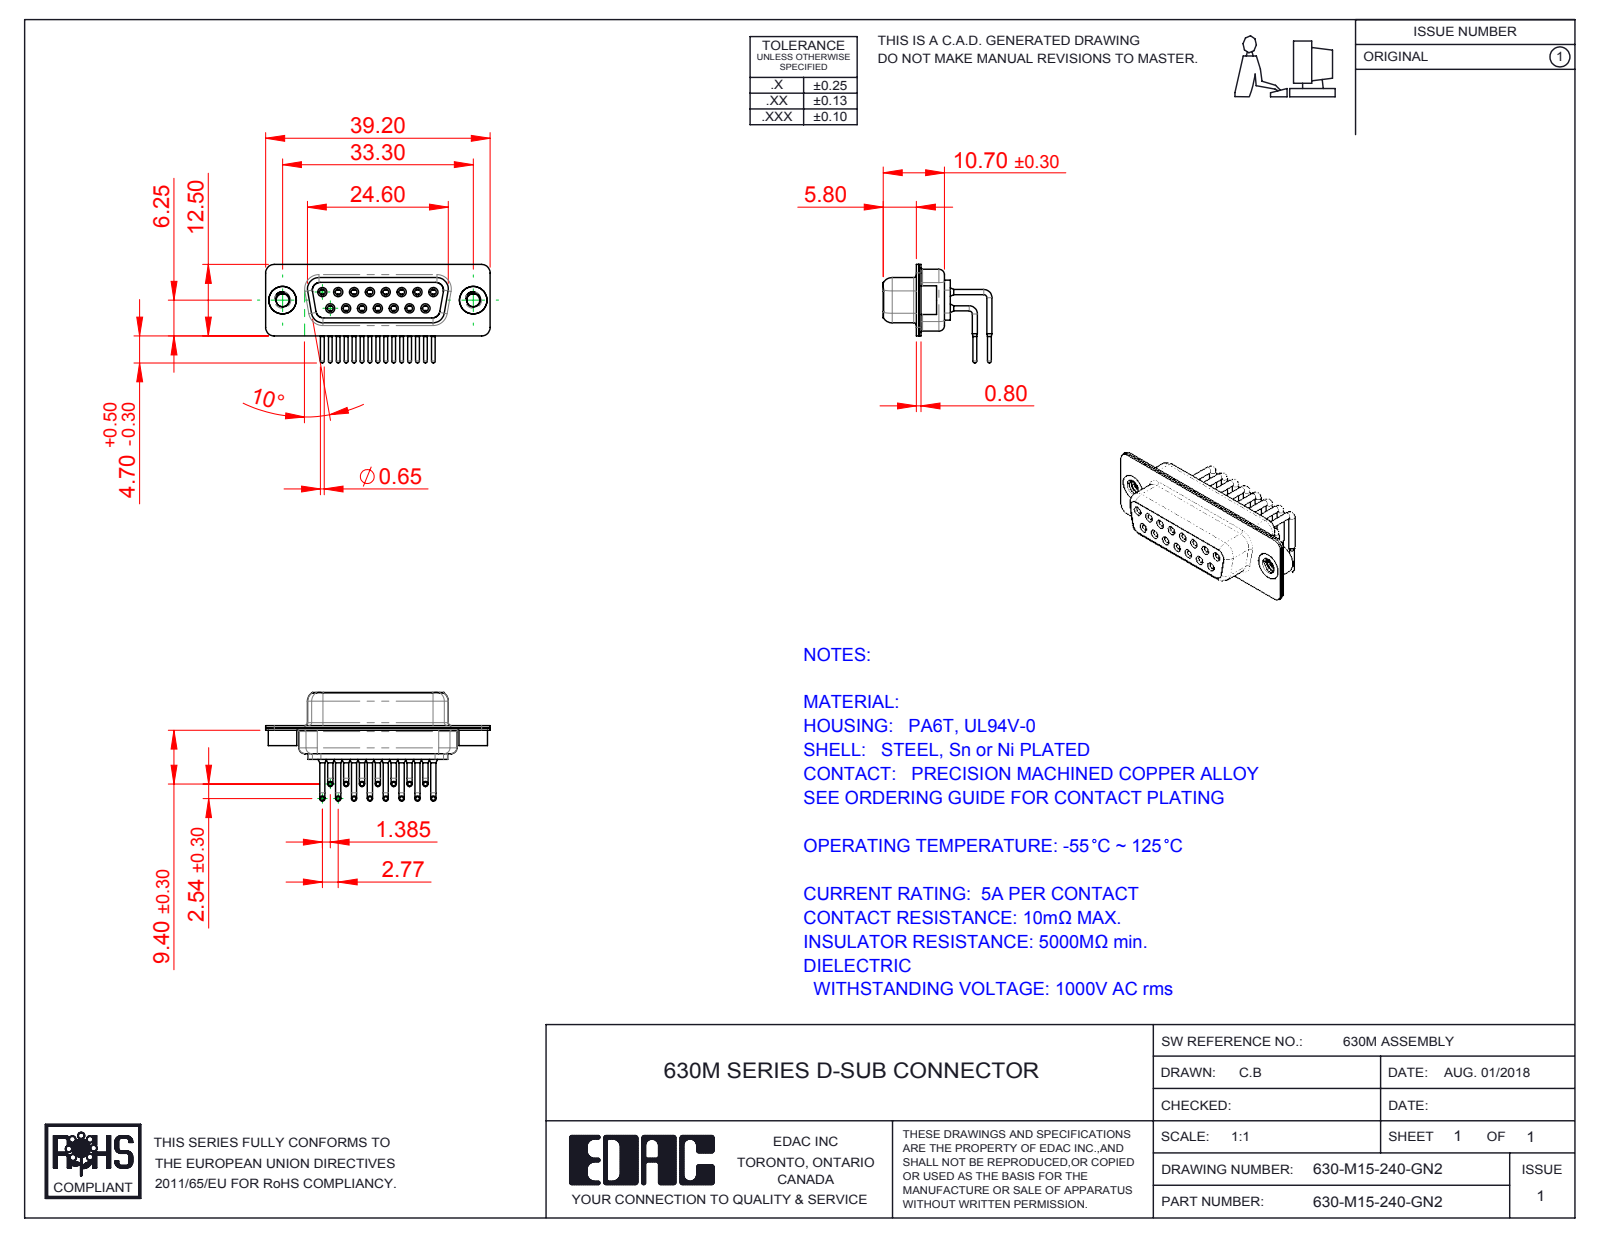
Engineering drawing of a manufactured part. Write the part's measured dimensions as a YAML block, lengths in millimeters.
part_name: "630-M15-240-GN2; 630M Shell Front_15 Contacts; 630M 4-40 Threaded Rivet; 630M Contact Row 1 (+3 more)"
step_written_by: "SolidWorks 2016 (CONFIG_CONTROL_DESIGN)"
units: millimeters
bodies: {solids: 20, faces: 1074, planar: 292, cylindrical: 482, other: 300}
overall_size: [39.2, 18.99, 17.2]
volume: 2568
surface_area: 6554
round_holes:
  - {diameter: 1, count: 15}
  - {diameter: 1.1, count: 15}
  - {diameter: 1.7, count: 15}
  - {diameter: 1.8, count: 15}
  - {diameter: 2, count: 15}
  - {diameter: 2.26, count: 2}
  - {diameter: 4, count: 2}
  - {diameter: 4.8, count: 2}
round_bosses_or_shafts:
  - {diameter: 0.9, count: 30}
  - {diameter: 1.6, count: 15}
  - {diameter: 1.5, count: 15}
  - {diameter: 0.65, count: 15}
  - {diameter: 5, count: 2}
  - {diameter: 4.9, count: 2}
partial_cylinders:
  - {radius: 1.5, count: 16}
  - {radius: 2, count: 12}
  - {radius: 1.35, count: 8}
  - {radius: 1.6, count: 8}
  - {radius: 0.25, count: 4}
  - {radius: 0.5, count: 4}
  - {radius: 0.6, count: 4}
  - {radius: 0.65, count: 4}
face_to_face_distances: [0.4, 1.45, 8.95, 2.3, 6.2, 0.8, 1.9, 8.5, 0.45, 7.05]
hole_center_spacings: [3.16, 2.77, 5.54, 8.31, 11.08, 5.03, 5.04, 7.48]
